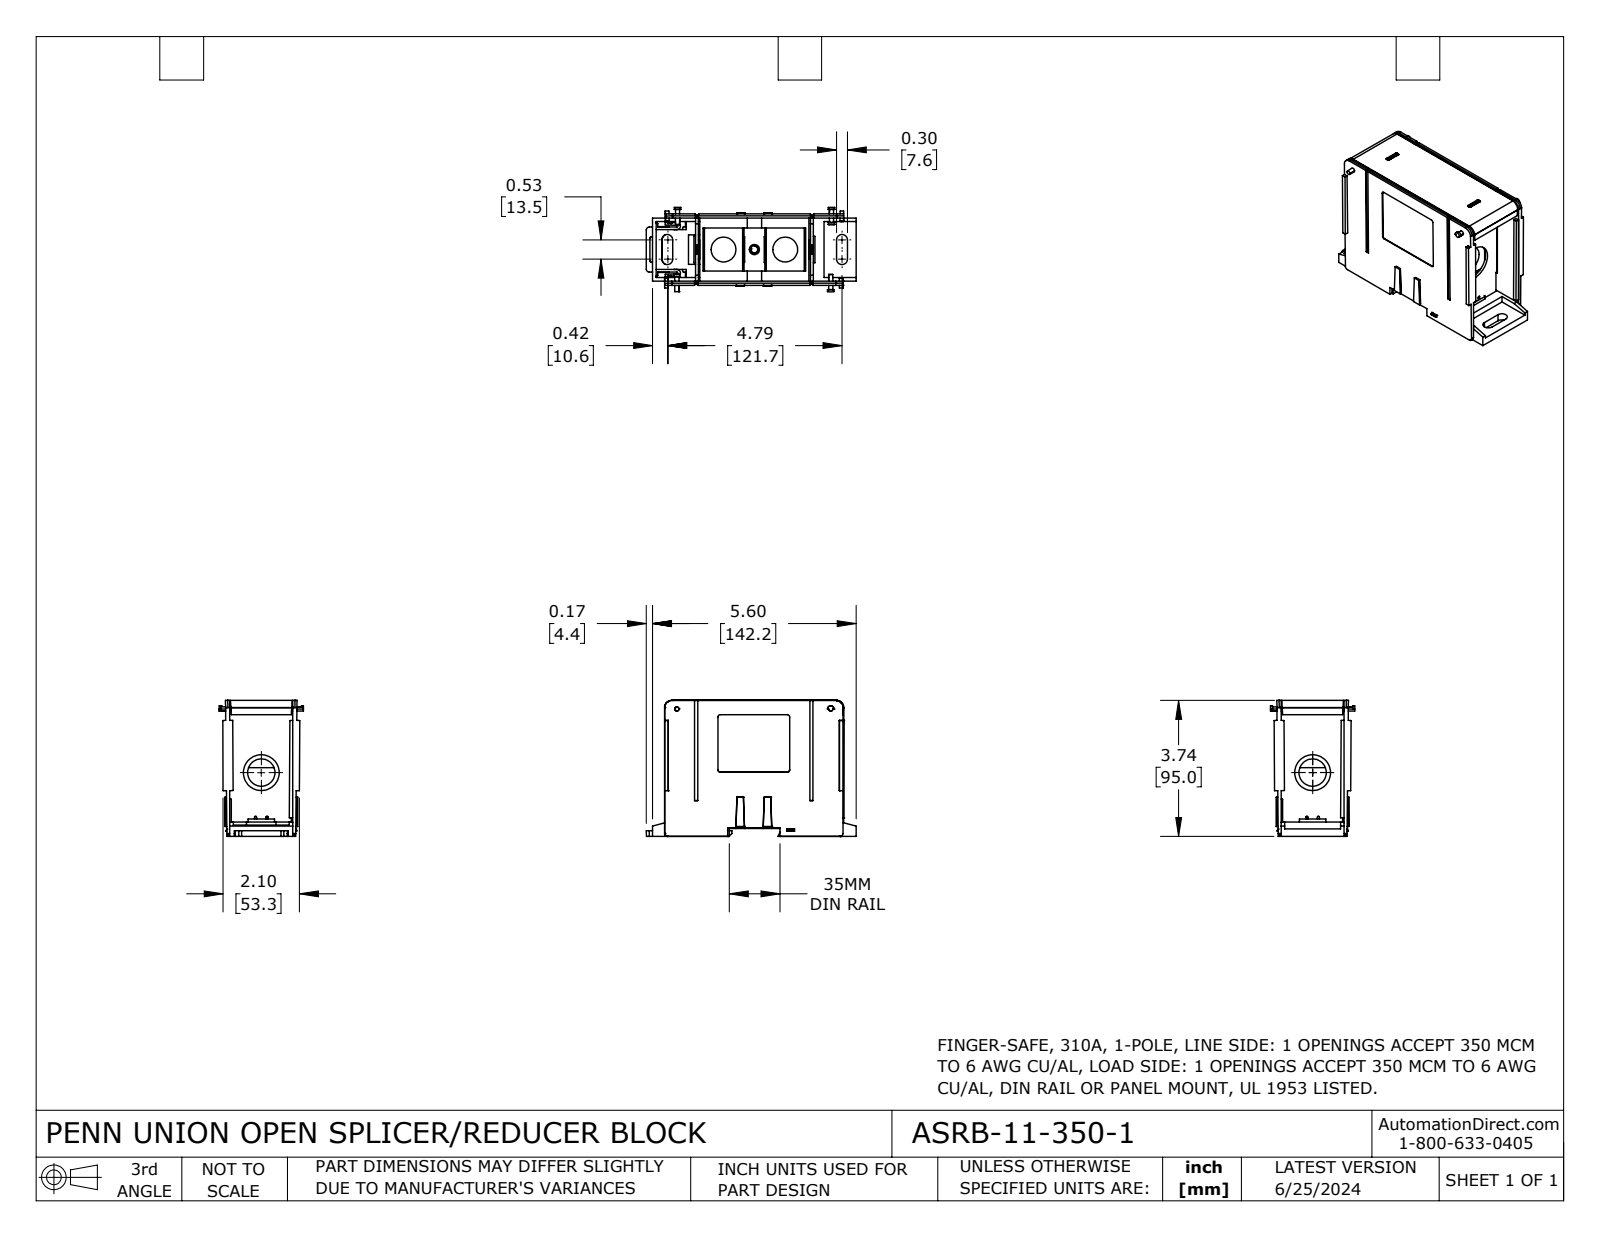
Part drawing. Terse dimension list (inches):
name: ASRB-11-350-1
written by: SolidWorks 2023 (CONFIG_CONTROL_DESIGN)
unit: in
bodies: 12 solids, 769 faces (546 planar, 147 cylindrical, 76 other)
size: 5.77 × 3.741 × 2.321
volume: 14 in³; area: 194.8 in²
holes: 2× ⌀0.682, 1× ⌀0.213, 1× ⌀0.28, 1× ⌀0.752, 1× ⌀0.984
rounds: 26× R0.039, 18× R0.059, 16× R0.02, 10× R0.079, 10× R0.197, 6× R0.012, 4× R0.089, 4× R0.15
face distances: 1.732, 0.079, 3.161, 0.276, 2.539, 2.468, 0.071, 0.02, 1.457, 0.295
hole spacings: 0.848, 1.697
